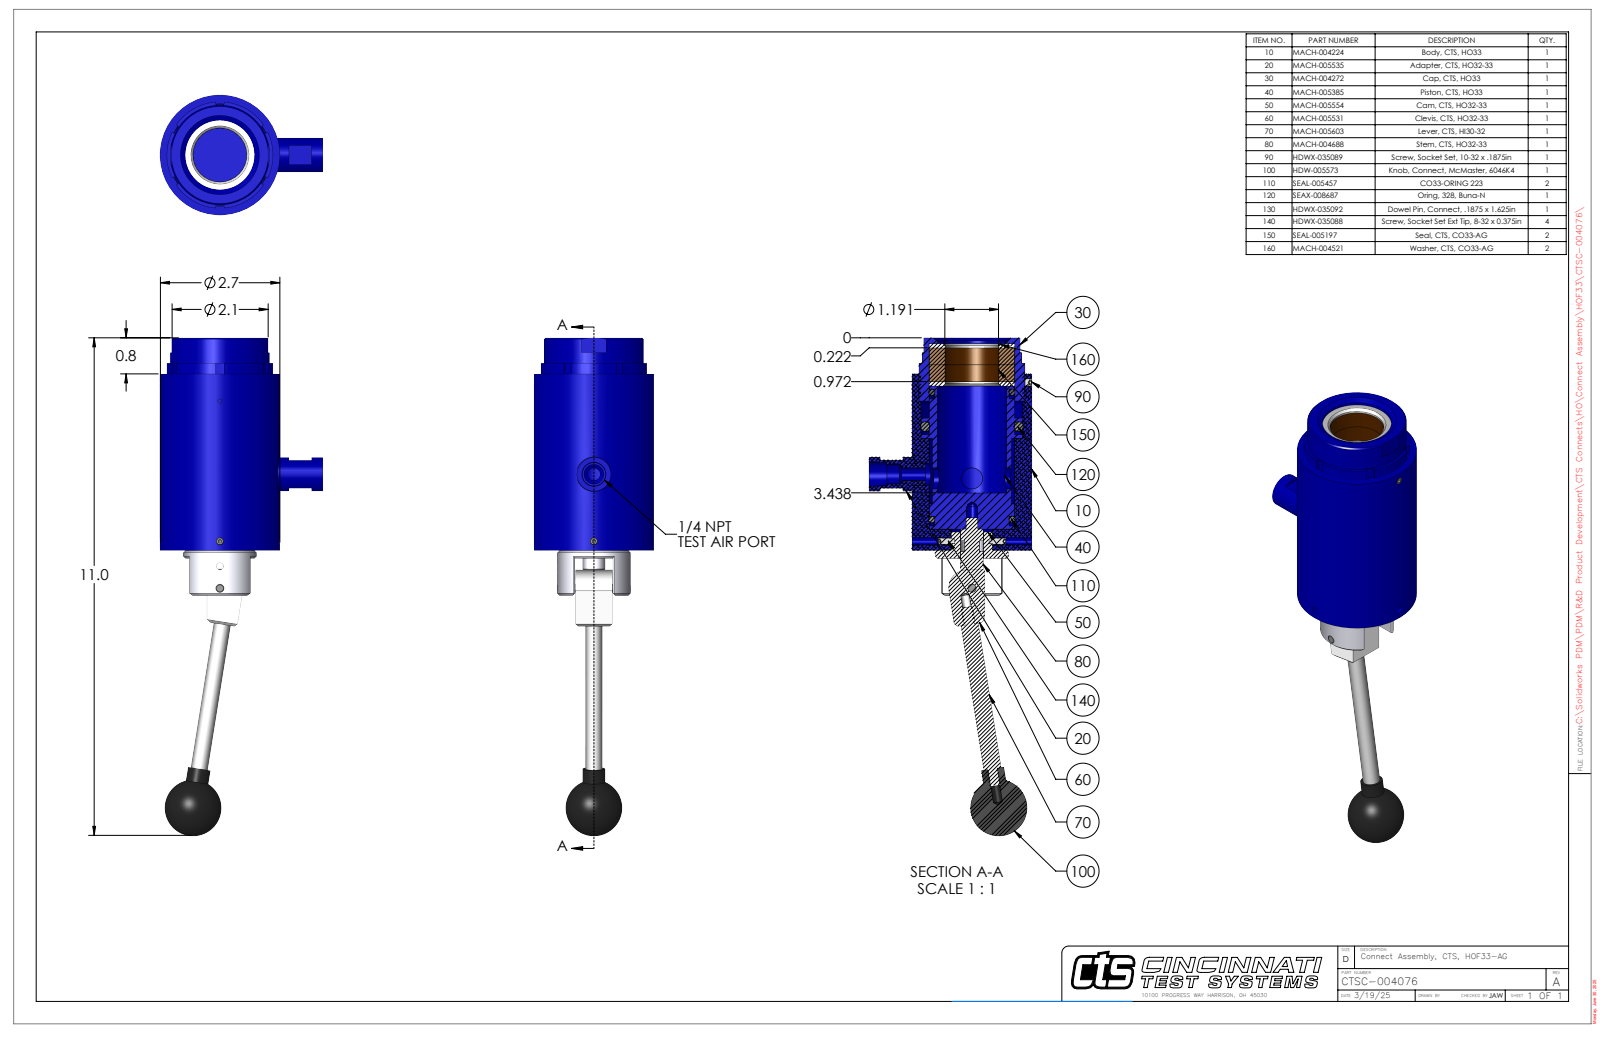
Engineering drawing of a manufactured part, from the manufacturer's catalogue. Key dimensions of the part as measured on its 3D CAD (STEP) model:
Part name (STEP PRODUCT): CTSC-004076
STEP written by: SolidWorks 2023 (AUTOMOTIVE_DESIGN)
Units: inches
Bodies: 15 solids, 546 faces (179 planar, 226 cylindrical, 141 other)
Overall size (bounding box): 11.035 × 3.6 × 2.65
Volume: 21.99 in³ · Surface area: 137.9 in²
Round holes (diameter × count): ⌀0.201 ×3, ⌀0.159 ×2, ⌀0.469 ×2, ⌀0.094 ×1, ⌀0.189 ×1, ⌀0.19 ×1, ⌀0.25 ×1, ⌀0.281 ×1, ⌀0.438 ×1, ⌀0.5 ×1, ⌀0.516 ×1, ⌀0.527 ×1
Round bosses / shafts (diameter × count): ⌀0.75 ×2, ⌀0.5 ×2, ⌀0.164 ×2, ⌀0.109 ×2, ⌀2.65 ×1, ⌀2.344 ×1, ⌀2.2 ×1, ⌀1.885 ×1
Partial cylindrical surfaces — rounded edges, fillets, slot ends (radius × count): R0.385 ×1, R0.4 ×1, R1.13 ×1, R1.185 ×1
Main face-to-face distances: 0.844, 0.094, 0.75, 3.736, 4.486, 0.375, 0.375, 4.111, 0.469, 3.642
Hole centre spacings: 0.093, 0.488, 1.713, 1.945, 2.033, 2.126, 2.433, 3.658
